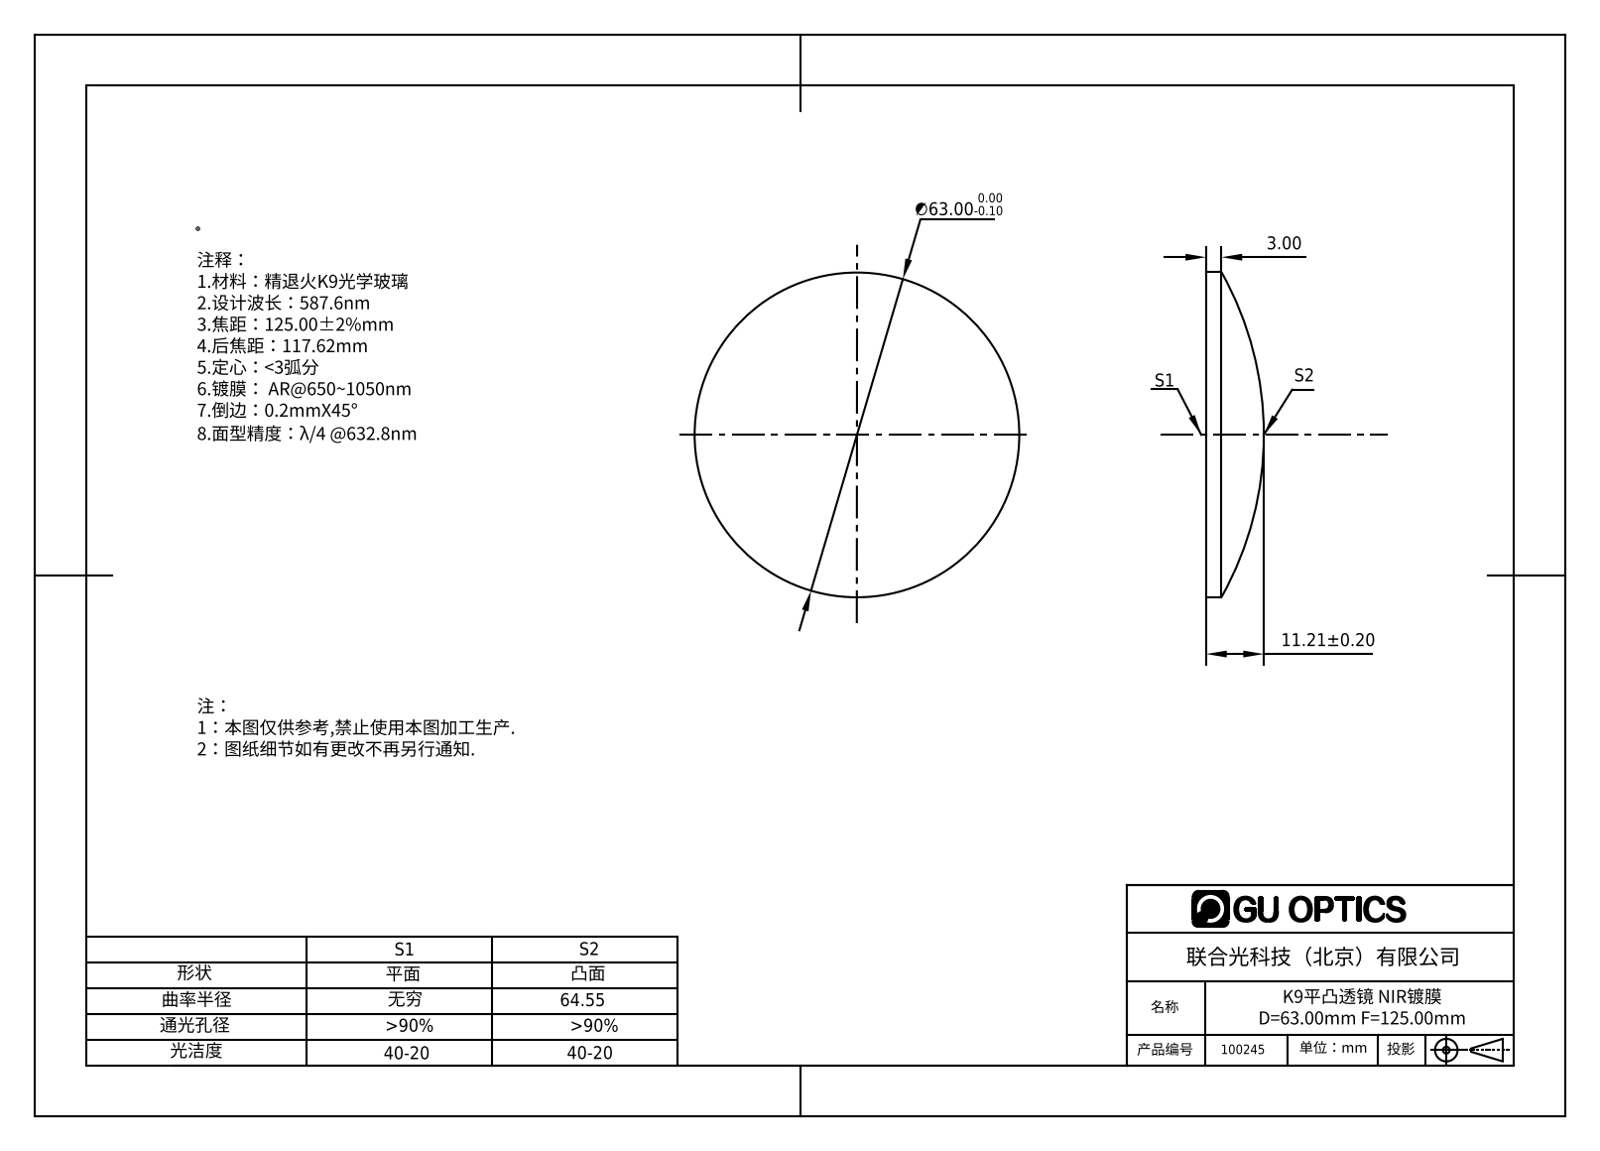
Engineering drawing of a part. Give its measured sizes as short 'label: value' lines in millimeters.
name: 100245
written by: SolidWorks 2016 (AUTOMOTIVE_DESIGN)
unit: mm
bodies: 1 solid, 5 faces (1 planar, 2 cylindrical, 2 other)
size: 63 × 63 × 11.21
volume: 22 438 mm³; area: 7 040 mm²
bosses: 1× ⌀63
